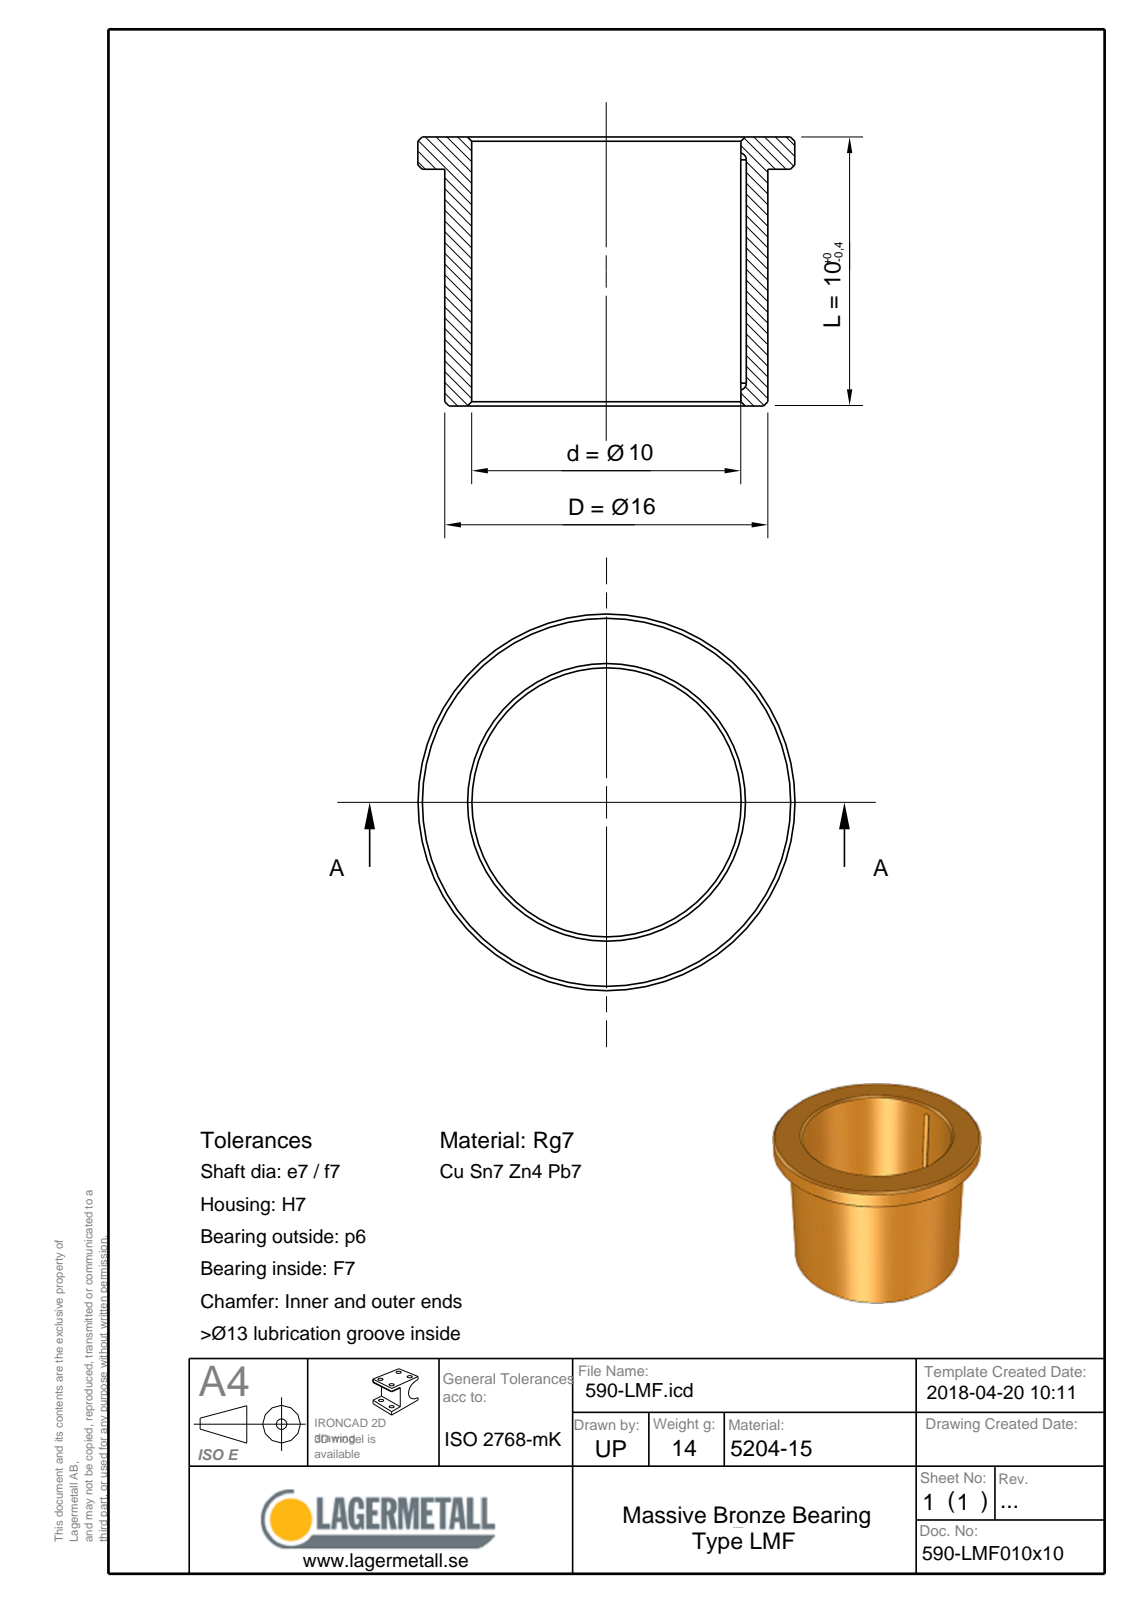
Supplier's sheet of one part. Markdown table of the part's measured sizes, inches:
| quantity | value |
| --- | --- |
| part name | 590-LMF010x10 |
| STEP written by | Spatial InterOp 3D (CONFIG_CONTROL_DESIGN) |
| units | inches |
| bodies | 1 solid, 11 faces (3 planar, 3 cylindrical, 5 other) |
| overall size | 0.787 × 0.787 × 0.394 |
| volume | 0.095 in³ |
| surface area | 1.99 in² |
| round holes (diameter × count) | 0.394 × 1 |
| round bosses / shafts (diameter × count) | 0.787 × 1, 0.63 × 1 |
| main face-to-face distances | 0.394, 0.276, 0.118 |
